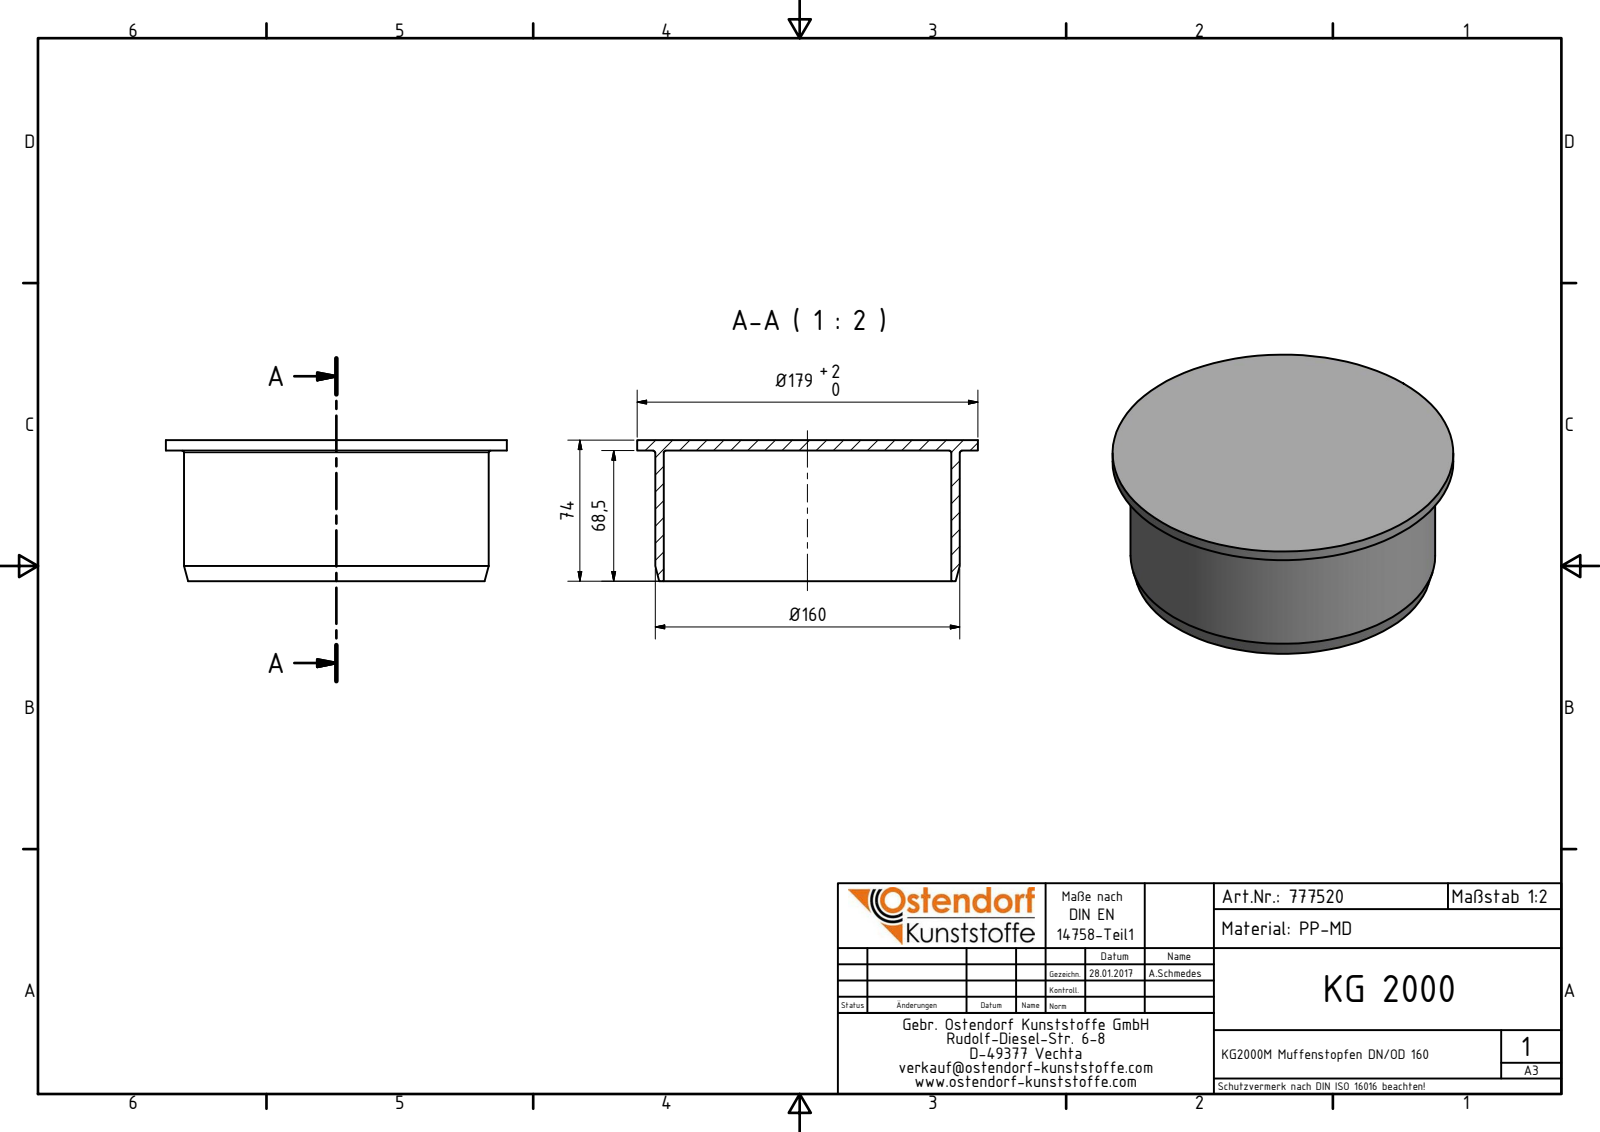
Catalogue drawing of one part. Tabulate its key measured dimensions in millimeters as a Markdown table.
| quantity | value |
| --- | --- |
| part name | 777520 KG2000M Muffenstopfen DN_OD 160 |
| STEP written by | Autodesk Inventor 2016 (AUTOMOTIVE_DESIGN) |
| units | millimeters |
| bodies | 1 solid, 10 faces (4 planar, 3 cylindrical, 3 other) |
| overall size | 179 × 179 × 74 |
| volume | 284 931 mm³ |
| surface area | 118 953 mm² |
| round holes (diameter × count) | 151 × 1 |
| round bosses / shafts (diameter × count) | 179 × 1, 160 × 1 |
| main face-to-face distances | 5.5, 68.5, 74 |
